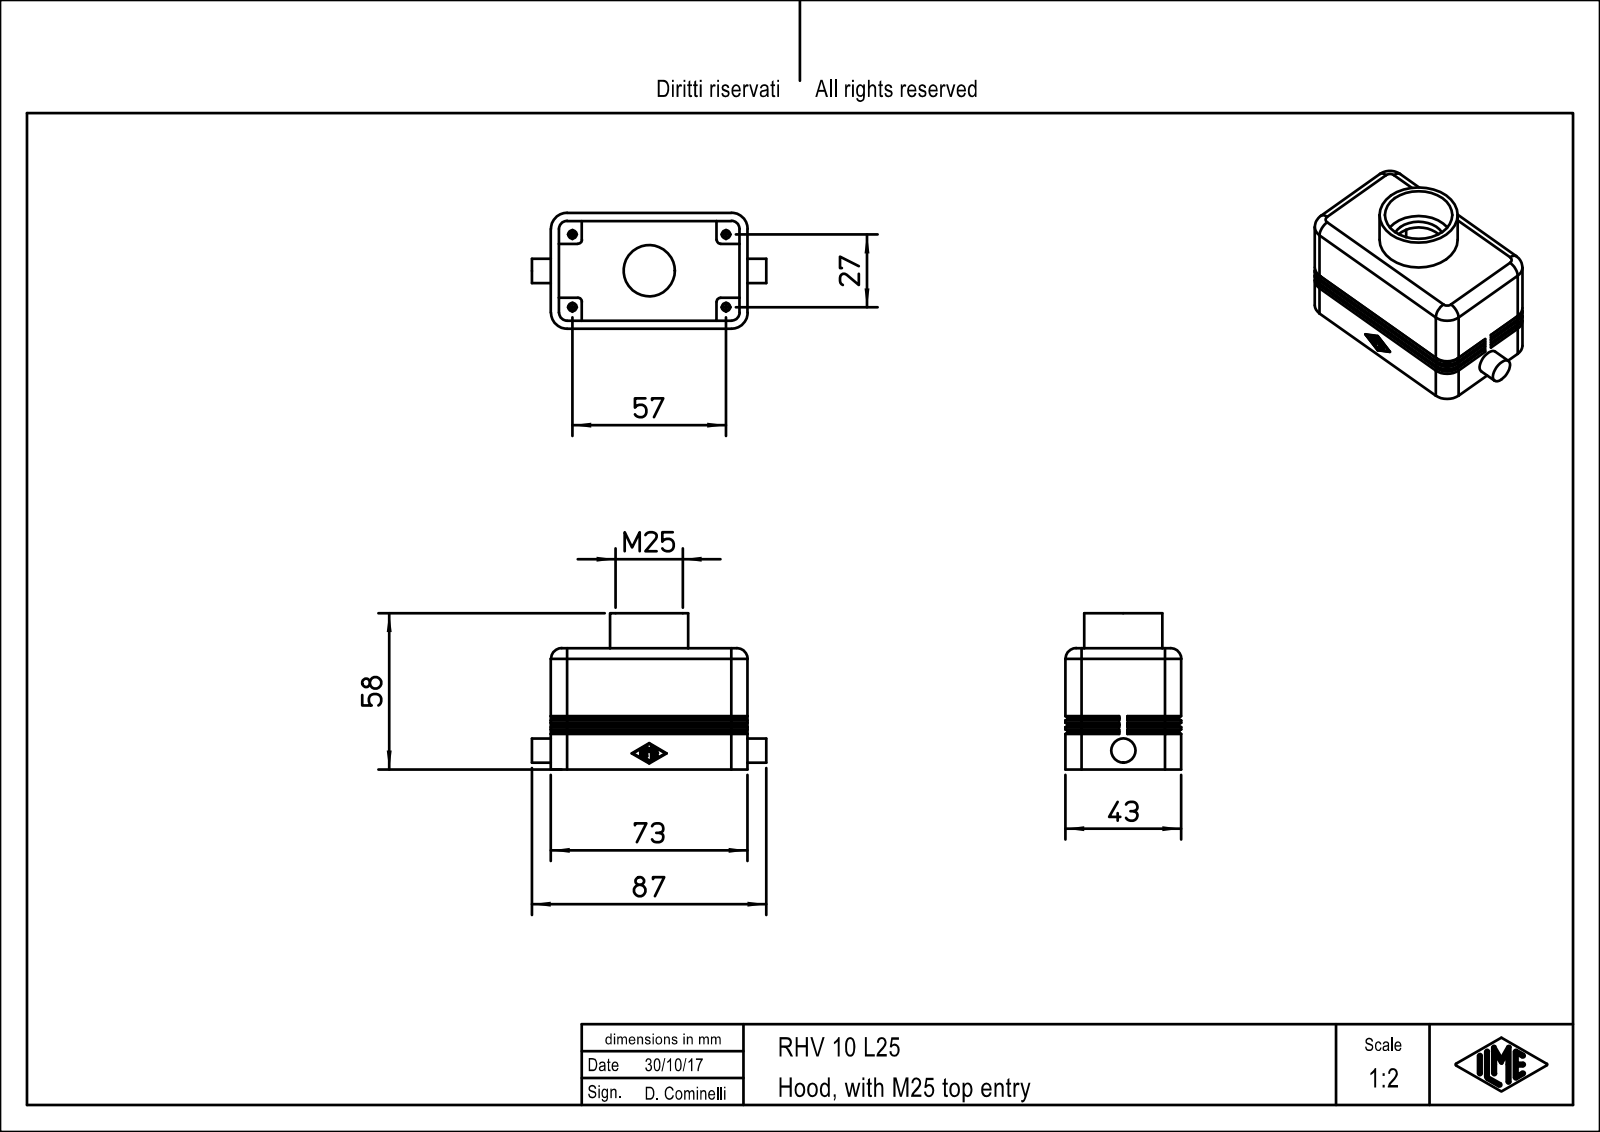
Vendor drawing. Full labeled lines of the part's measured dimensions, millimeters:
Part name (STEP PRODUCT): RHV_10_L25
STEP written by: PTC Creo Elements/Direct Modeling 19.0E 27-Jun-2016 (C) Parametric Technology GmbH (AUTOMOTIVE_DESIGN)
Units: millimetres
Bodies: 1 solid, 316 faces (140 planar, 116 cylindrical, 60 other)
Overall size (bounding box): 87 × 58 × 43
Volume: 45 895 mm³ · Surface area: 27 638 mm²
Round holes (diameter × count): ⌀2.46 ×4, ⌀3.1 ×4, ⌀19 ×1, ⌀25 ×1
Round bosses / shafts (diameter × count): ⌀29 ×1, ⌀9 ×1
Partial cylindrical surfaces — rounded edges, fillets, slot ends (radius × count): R0.4 ×24, R0.25 ×14, R1.5 ×4, R3 ×4, R4 ×4, R5 ×4, R6 ×4
Main face-to-face distances: 3, 40, 37, 43, 70, 11.5, 8.5, 73, 67, 31.5
Hole centre spacings: 31.54, 27, 57, 63.07
